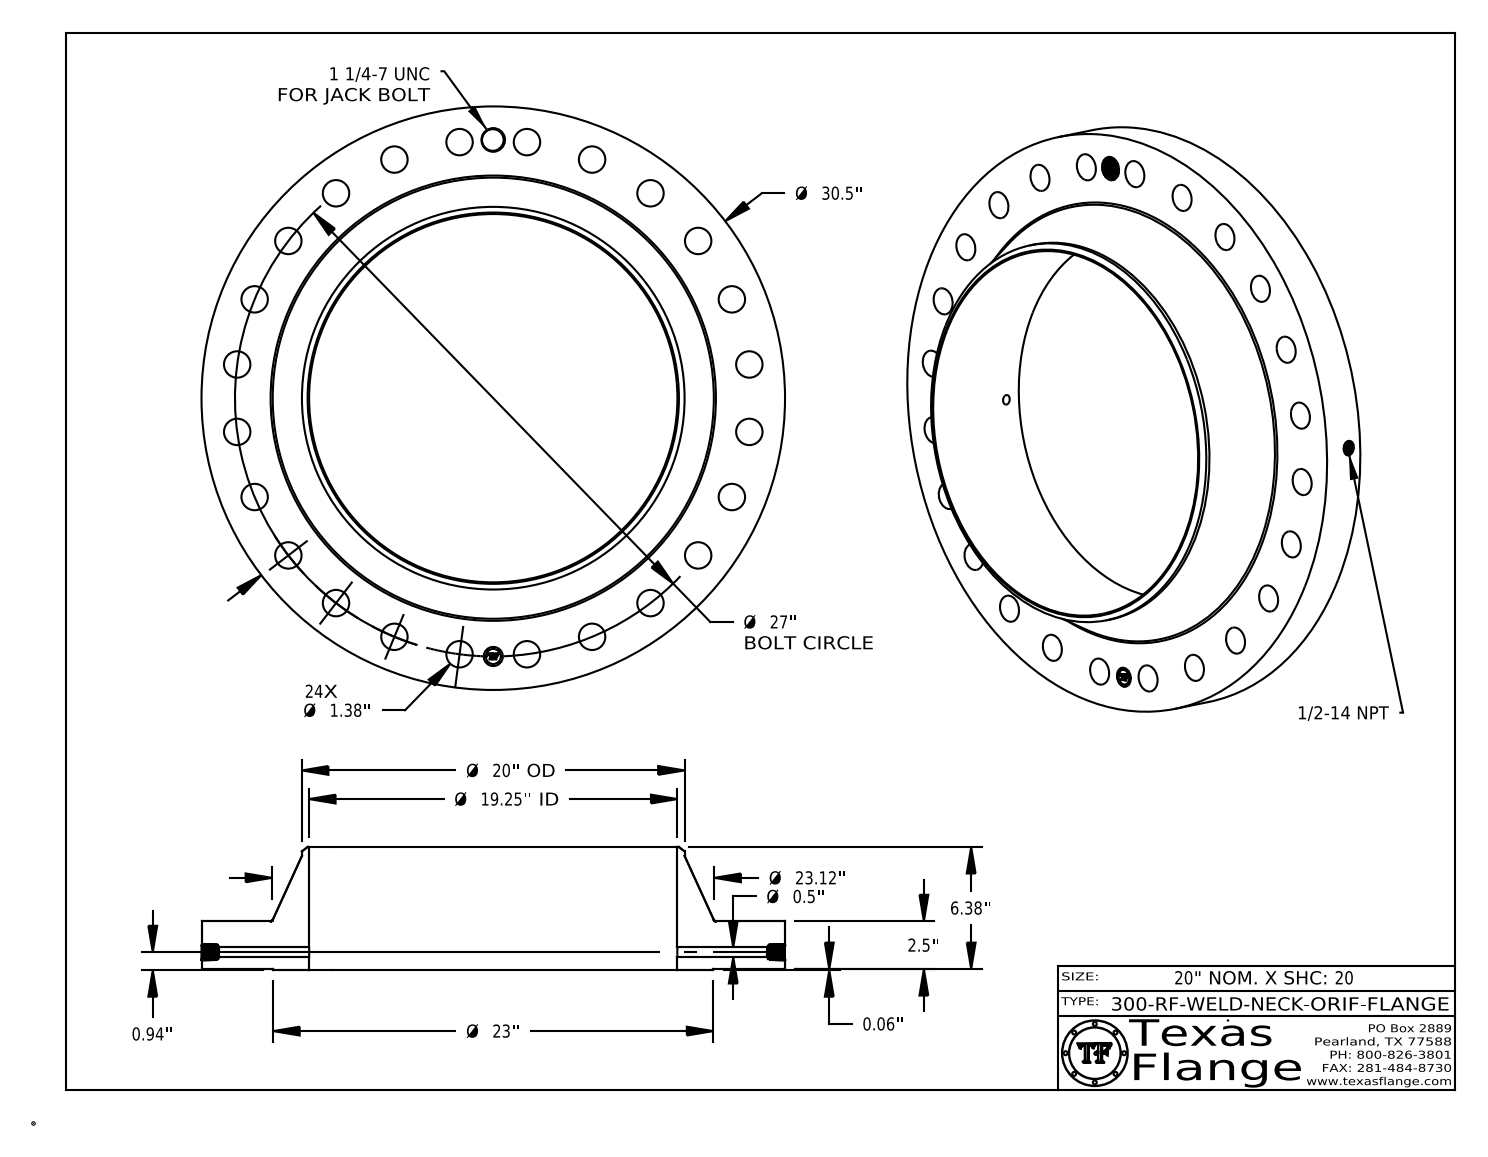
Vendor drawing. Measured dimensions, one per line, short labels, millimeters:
name: 300-RF-WELD-NECK
written by: CATIA V5 STEP AP214 (AUTOMOTIVE_DESIGN)
unit: mm
bodies: 1 solid, 818 faces (369 planar, 131 cylindrical, 318 other)
size: 774.7 × 774.7 × 163.6
volume: 20 890 000 mm³; area: 1 226 000 mm²
holes: 24× ⌀35.1, 1× ⌀12.7, 1× ⌀17.1, 1× ⌀25.4, 1× ⌀28.2, 1× ⌀489
bosses: 8× ⌀1.5, 1× ⌀774.7, 1× ⌀584.2, 1× ⌀508, 1× ⌀20
face distances: 63.5, 1.5, 65, 163.6, 162.1, 98.6, 64.6, 63.1, 0.4, 98.9
hole spacings: 342.9, 593.9, 633.6, 544.1, 89.5, 177.5, 484.9, 662.4
